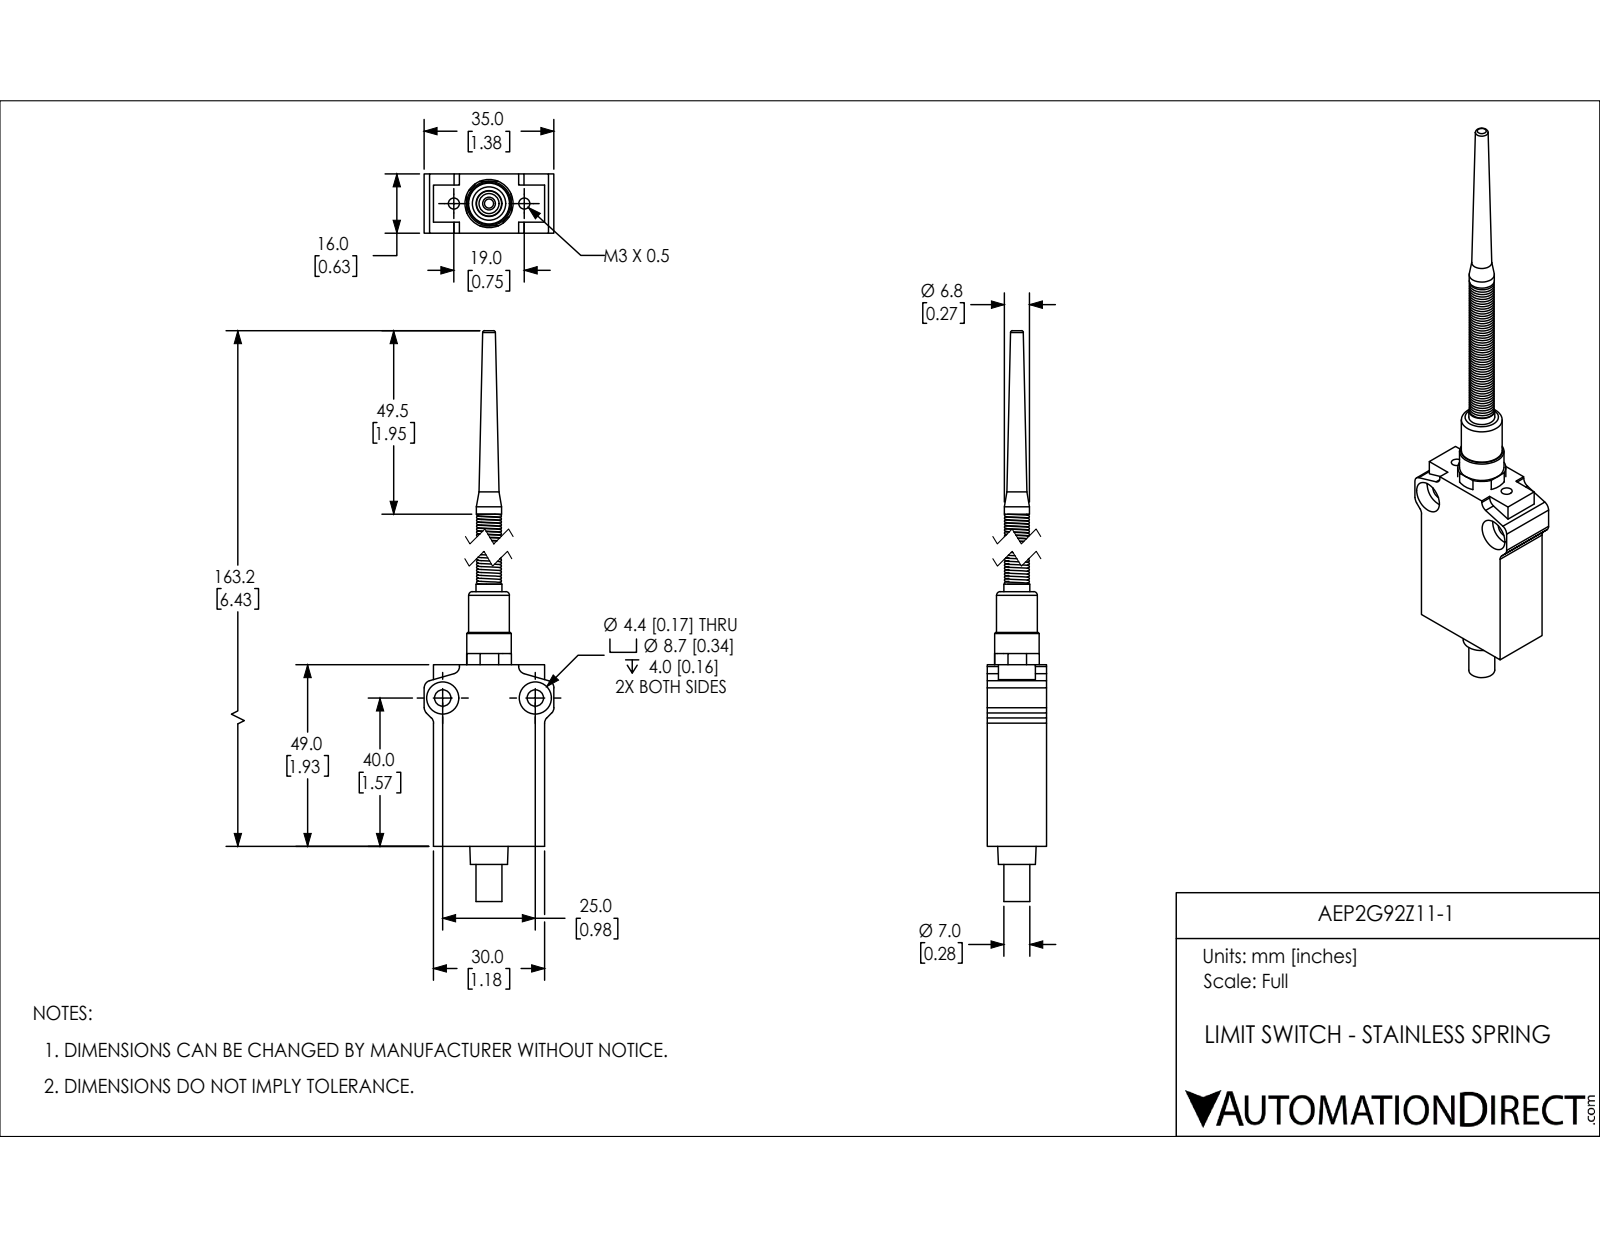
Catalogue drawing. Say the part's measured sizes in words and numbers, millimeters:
The part is named "AEP2G92Z11-1". Its 3-D file was written by "SolidWorks 2018 (AUTOMOTIVE_DESIGN)". It is 4 solids with 131 faces: 53 planar, 59 cylindrical and 19 other. Overall it measures 178.1 by 35 by 16 millimeters. Its volume is 26 576 cubic millimeters and its surface area 10 906 square millimeters. Round holes: 2 of diameter 3, 2 of diameter 4.4, 2 of diameter 8.7, 1 of diameter 13. Round bosses or shafts: 1 of diameter 12, 1 of diameter 11, 1 of diameter 7, 1 of diameter 6.8. Partial cylindrical surfaces (rounded edges, fillets, slot ends): 8 of radius 2. The main face-to-face distances are 16, 30, 12, 49, 3, 4, 2.5, 32.5, 4.8, 1.8. The hole center spacings are 9.5, 19, 25.
